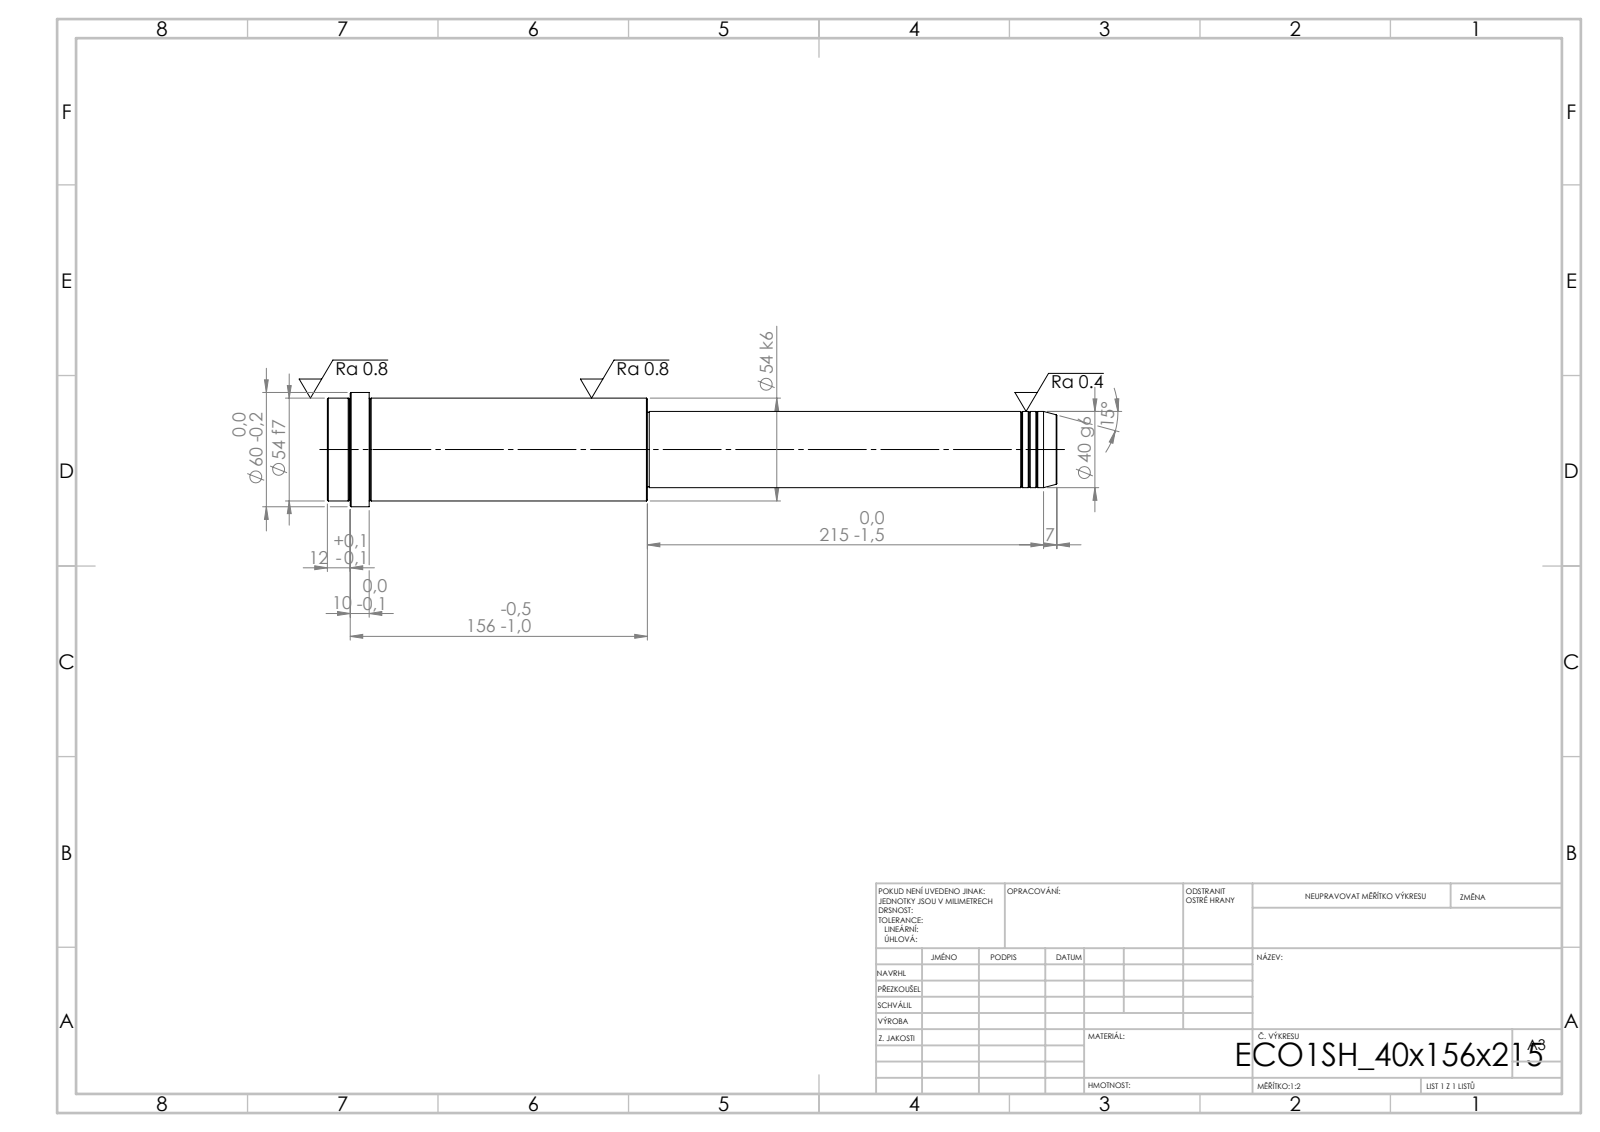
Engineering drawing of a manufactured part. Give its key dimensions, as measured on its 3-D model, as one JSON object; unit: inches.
{"step_written_by": "SolidWorks 2019 (CONFIG_CONTROL_DESIGN)", "units": "inches", "bodies": {"solids": 1, "faces": 52, "planar": 6, "cylindrical": 16, "other": 30}, "overall_size": [15.079, 2.362, 2.362], "volume_in3": 40.22, "surface_area_in2": 95.28, "round_bosses_or_shafts": [[2.362, 1], [2.126, 1], [1.575, 1], [1.535, 1]], "face_to_face_distances": [6.614, 8.465, 15.079, 14.213, 5.748, 0.866, 14.606, 6.142, 0.394, 0.472]}
